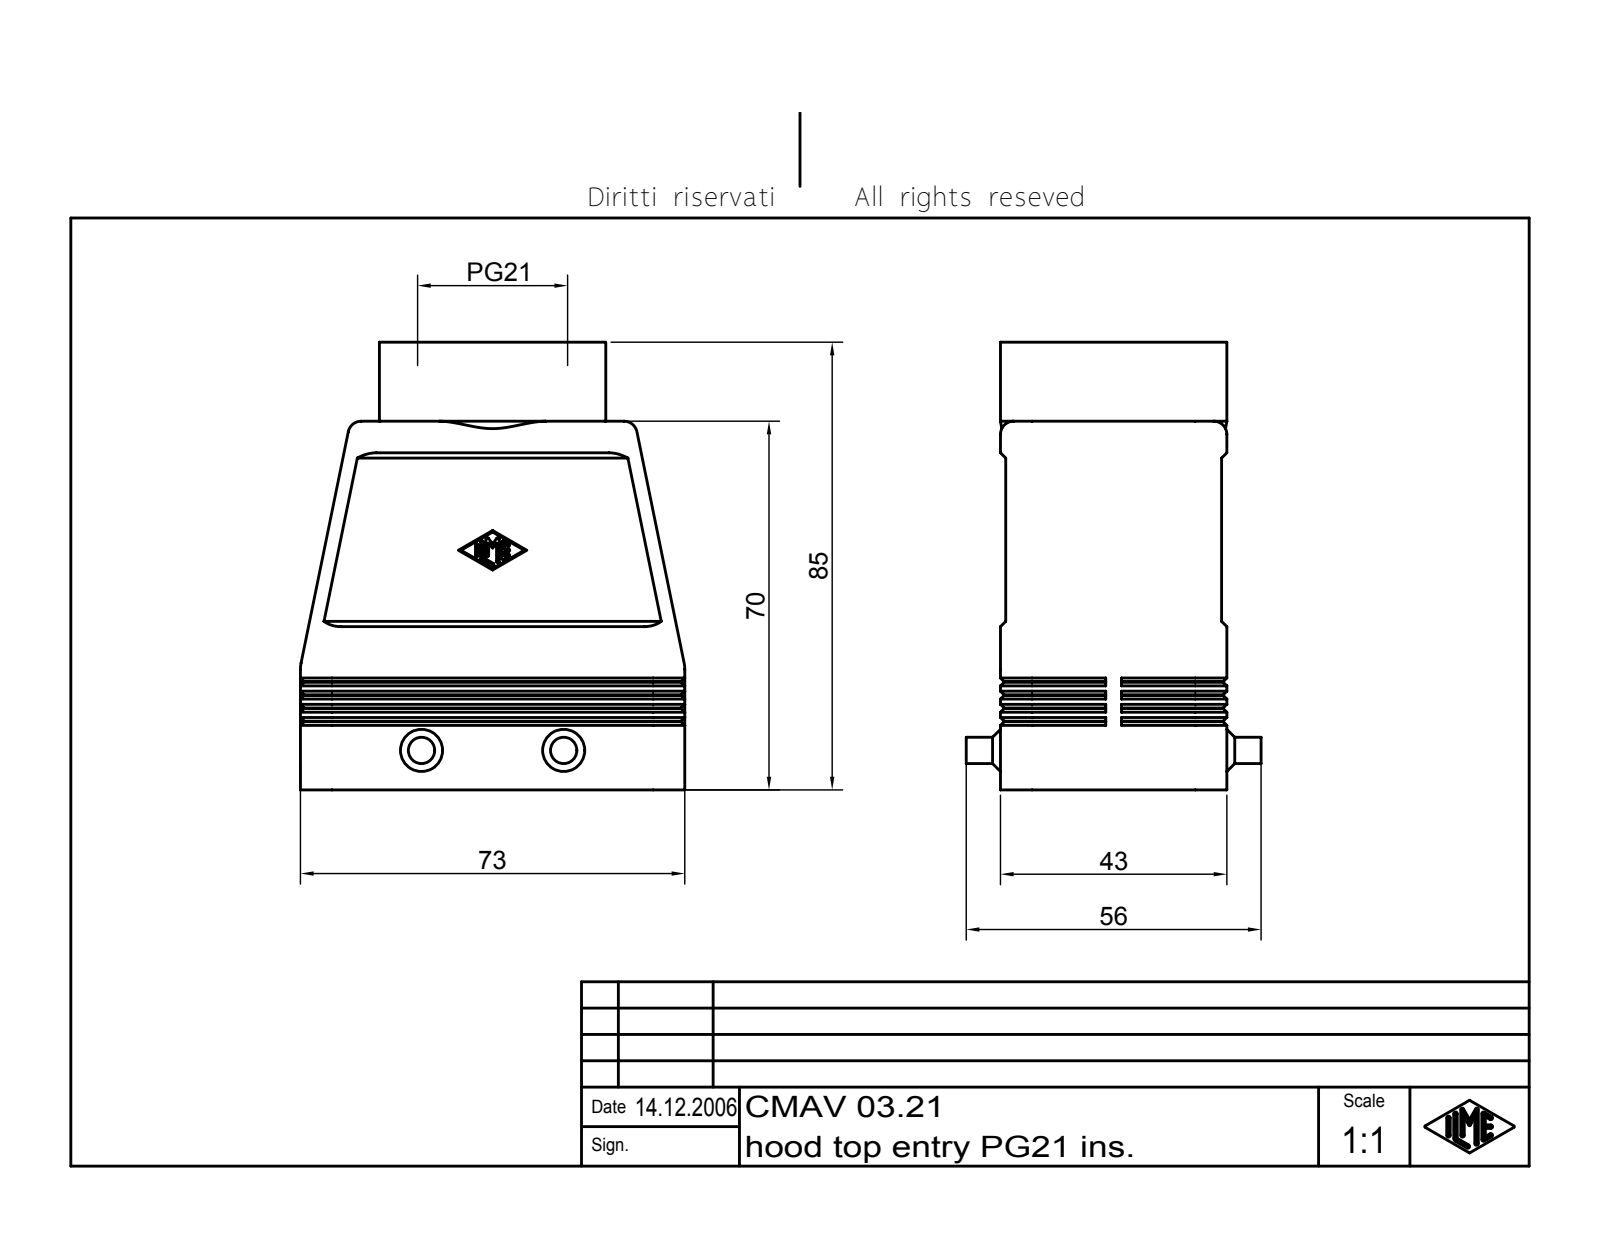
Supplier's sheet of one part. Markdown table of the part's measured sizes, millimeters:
| quantity | value |
| --- | --- |
| part name | CAO Tüllengehäuse 2 Bügel für einen Einsatz |
| STEP written by | Autodesk Inventor 7 (AUTOMOTIVE_DESIGN) |
| units | millimeters |
| bodies | 1 solid, 415 faces (153 planar, 108 cylindrical, 154 other) |
| overall size | 85 × 73 × 56 |
| volume | 66 437 mm³ |
| surface area | 36 681 mm² |
| round holes (diameter × count) | 24.78 × 1, 26.78 × 1 |
| round bosses / shafts (diameter × count) | 5 × 2, 43 × 1, 25.78 × 1 |
| partial cylindrical surfaces (radius × count) | 0.25 × 14, 6 × 10, 2 × 4, 2.5 × 4, 3 × 4, 5.3 × 2 |
| main face-to-face distances | 3, 2, 1, 39, 37, 40, 42, 9, 12, 41 |
